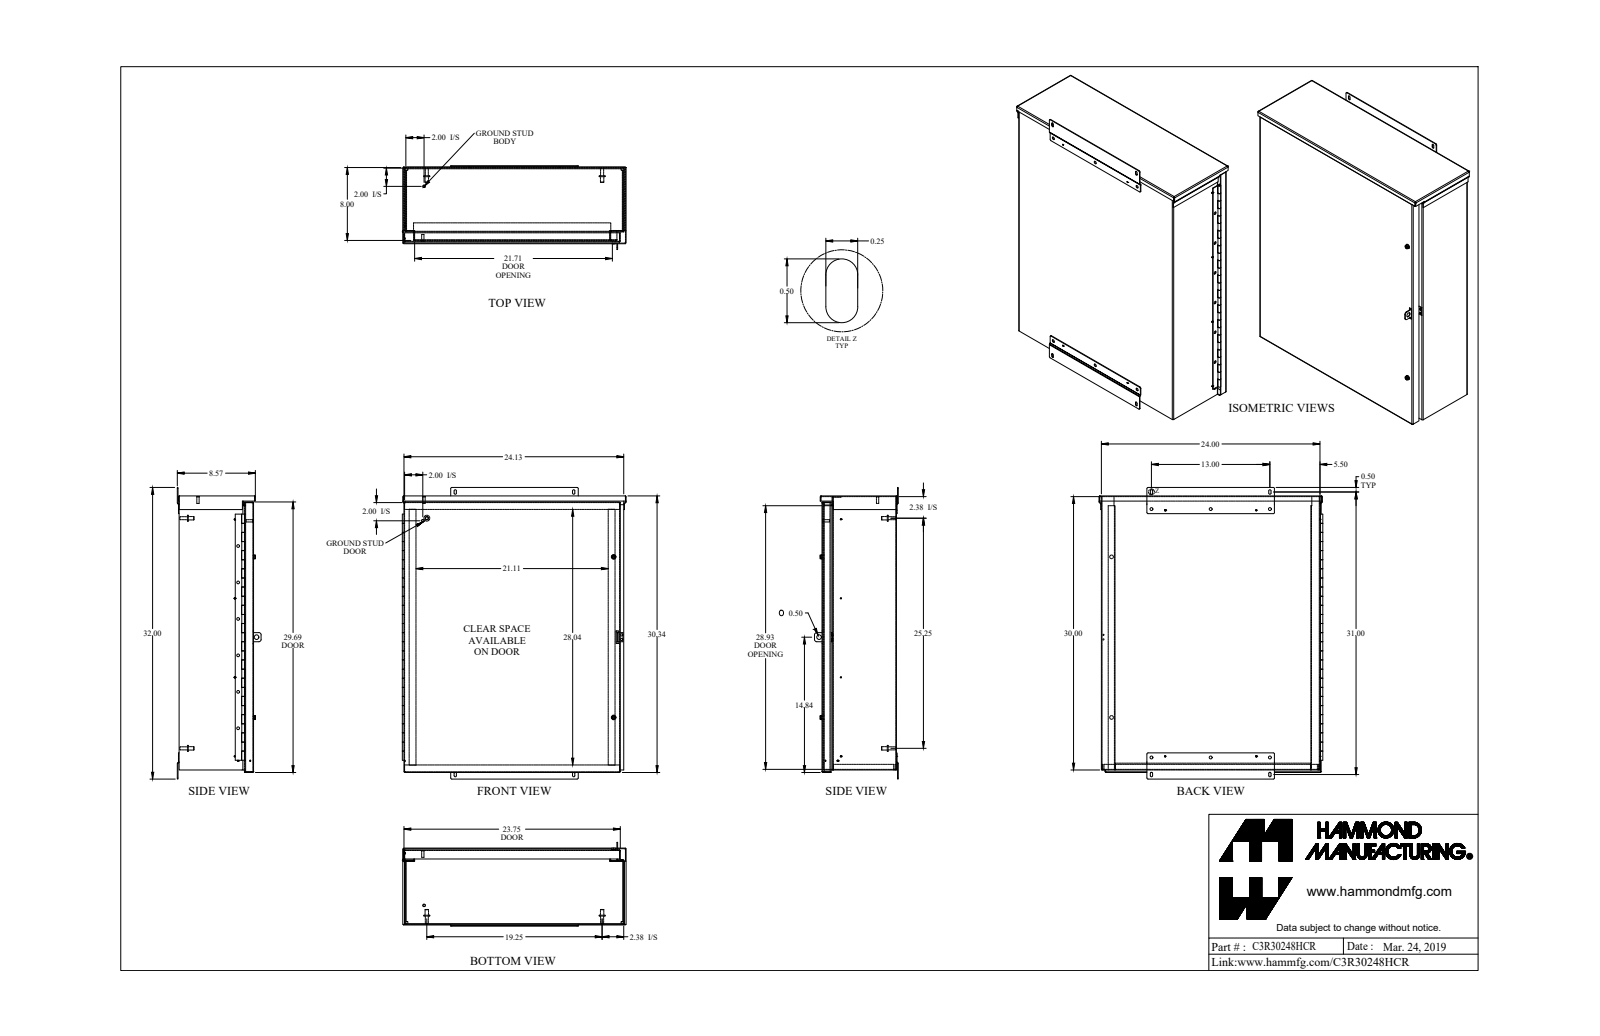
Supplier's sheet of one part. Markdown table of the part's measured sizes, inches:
| quantity | value |
| --- | --- |
| part name | C3R30248HCR_Default |
| STEP written by | SolidWorks 2019 (CONFIG_CONTROL_DESIGN) |
| units | inches |
| bodies | 33 solids, 942 faces (517 planar, 371 cylindrical, 54 other) |
| overall size | 32 × 24.571 × 9.197 |
| volume | 213.5 in³ |
| surface area | 5 777 in² |
| round holes (diameter × count) | 0.313 × 9, 0.304 × 6, 0.137 × 4, 0.14 × 4, 0.26 × 3, 0.266 × 2, 0.28 × 2, 0.29 × 2, 0.397 × 2, 0.188 × 1, 0.5 × 1 |
| round bosses / shafts (diameter × count) | 0.131 × 10, 0.65 × 4, 0.375 × 4, 0.33 × 4, 0.51 × 3, 0.244 × 3, 0.187 × 3, 0.5 × 2 |
| partial cylindrical surfaces (radius × count) | 0.036 × 31, 0.108 × 31, 0.125 × 19, 0.171 × 3, 0.25 × 2 |
| main face-to-face distances | 0.072, 8.1, 8.028, 8.172, 23.928, 30, 24, 23.856, 29.928, 30.072 |
| hole center spacings | 4, 1.505, 5.002, 6.5, 8, 11.501, 27.582, 12 |
